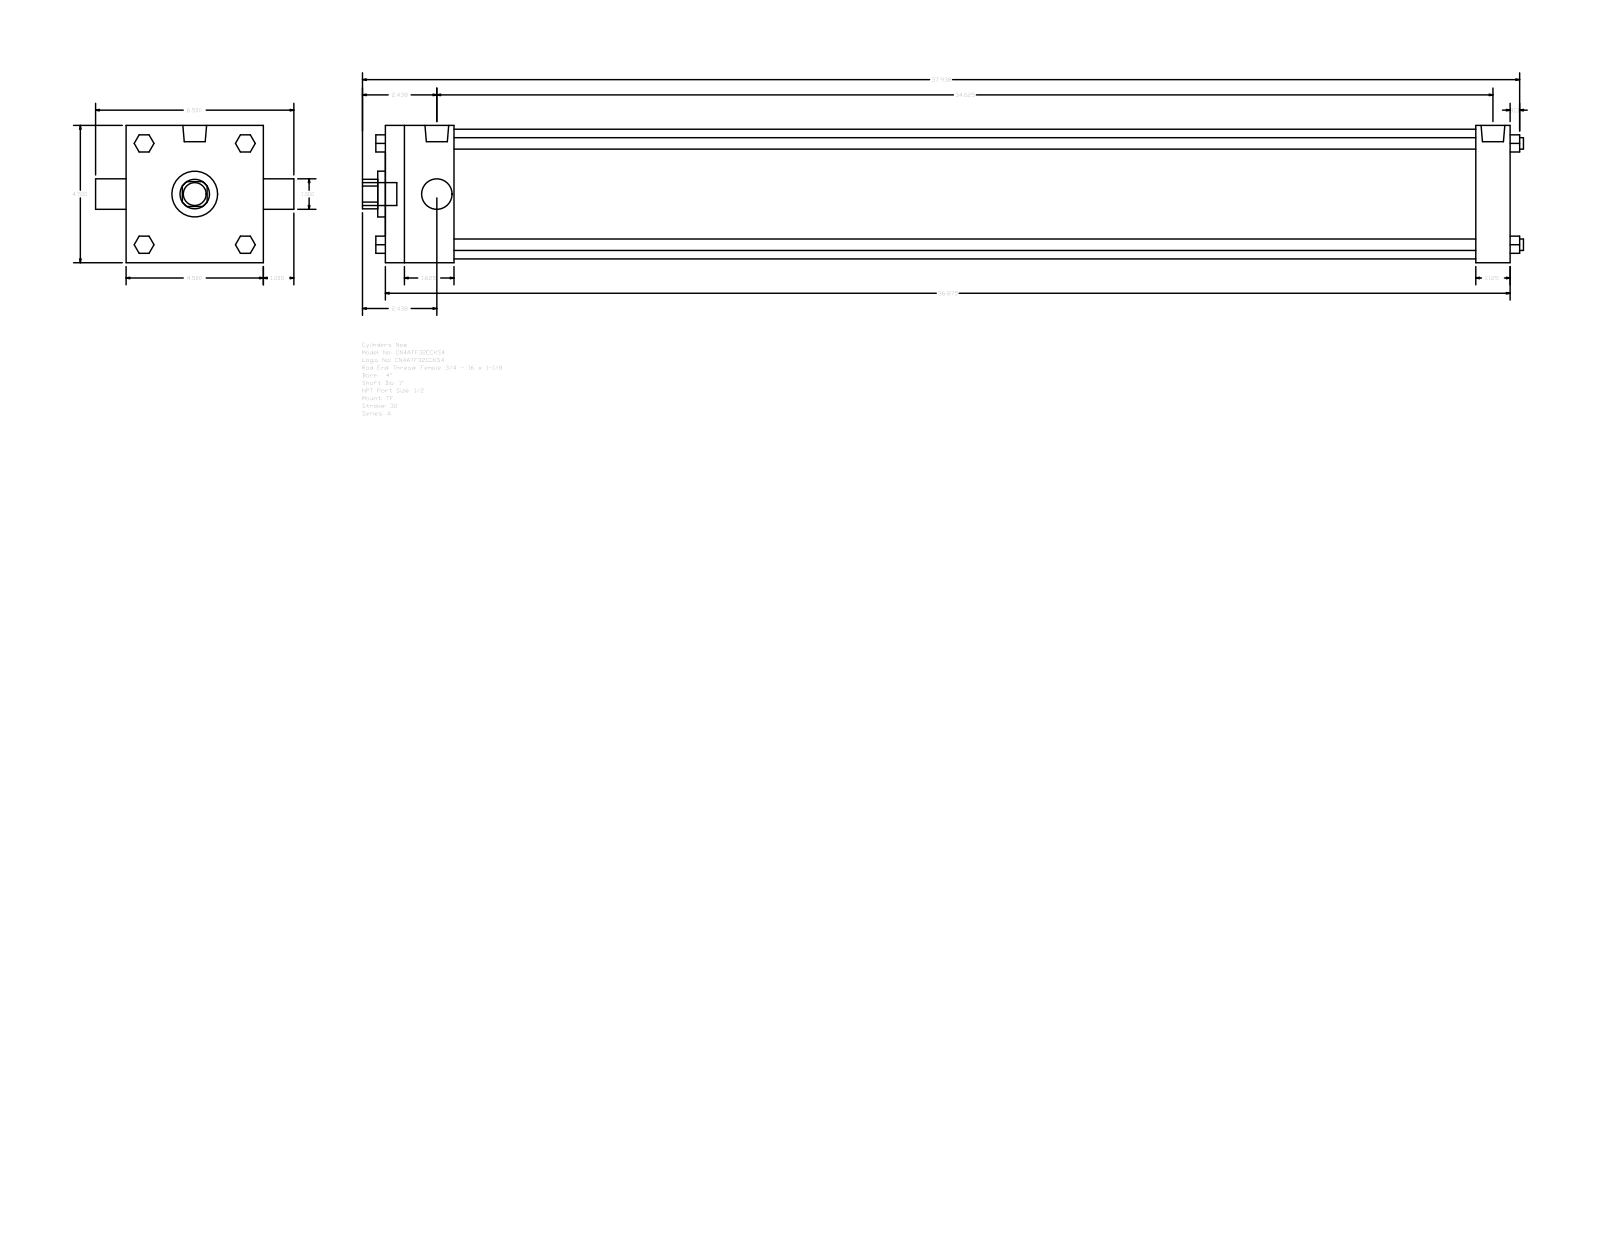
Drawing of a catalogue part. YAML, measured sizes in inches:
part_name: "A_TF__0400_1"
step_written_by: "GSSL Pune (CONFIG_CONTROL_DESIGN)"
units: inches
bodies: {solids: 0, faces: 120, planar: 92, cylindrical: 28, other: 0}
overall_size: [38.063, 6.5, 4.5]
round_holes:
  - {diameter: 1, count: 2}
  - {diameter: 1.5, count: 1}
  - {diameter: 4.25, count: 1}
round_bosses_or_shafts:
  - {diameter: 0.375, count: 4}
  - {diameter: 0.344, count: 3}
  - {diameter: 0.778, count: 2}
  - {diameter: 0.75, count: 1}
partial_cylinders:
  - {radius: 0.484, count: 1}
face_to_face_distances: [4.5, 36.875, 1.125, 35.75, 2.25, 33.5, 34.625, 0.563, 1.66, 2.875]
